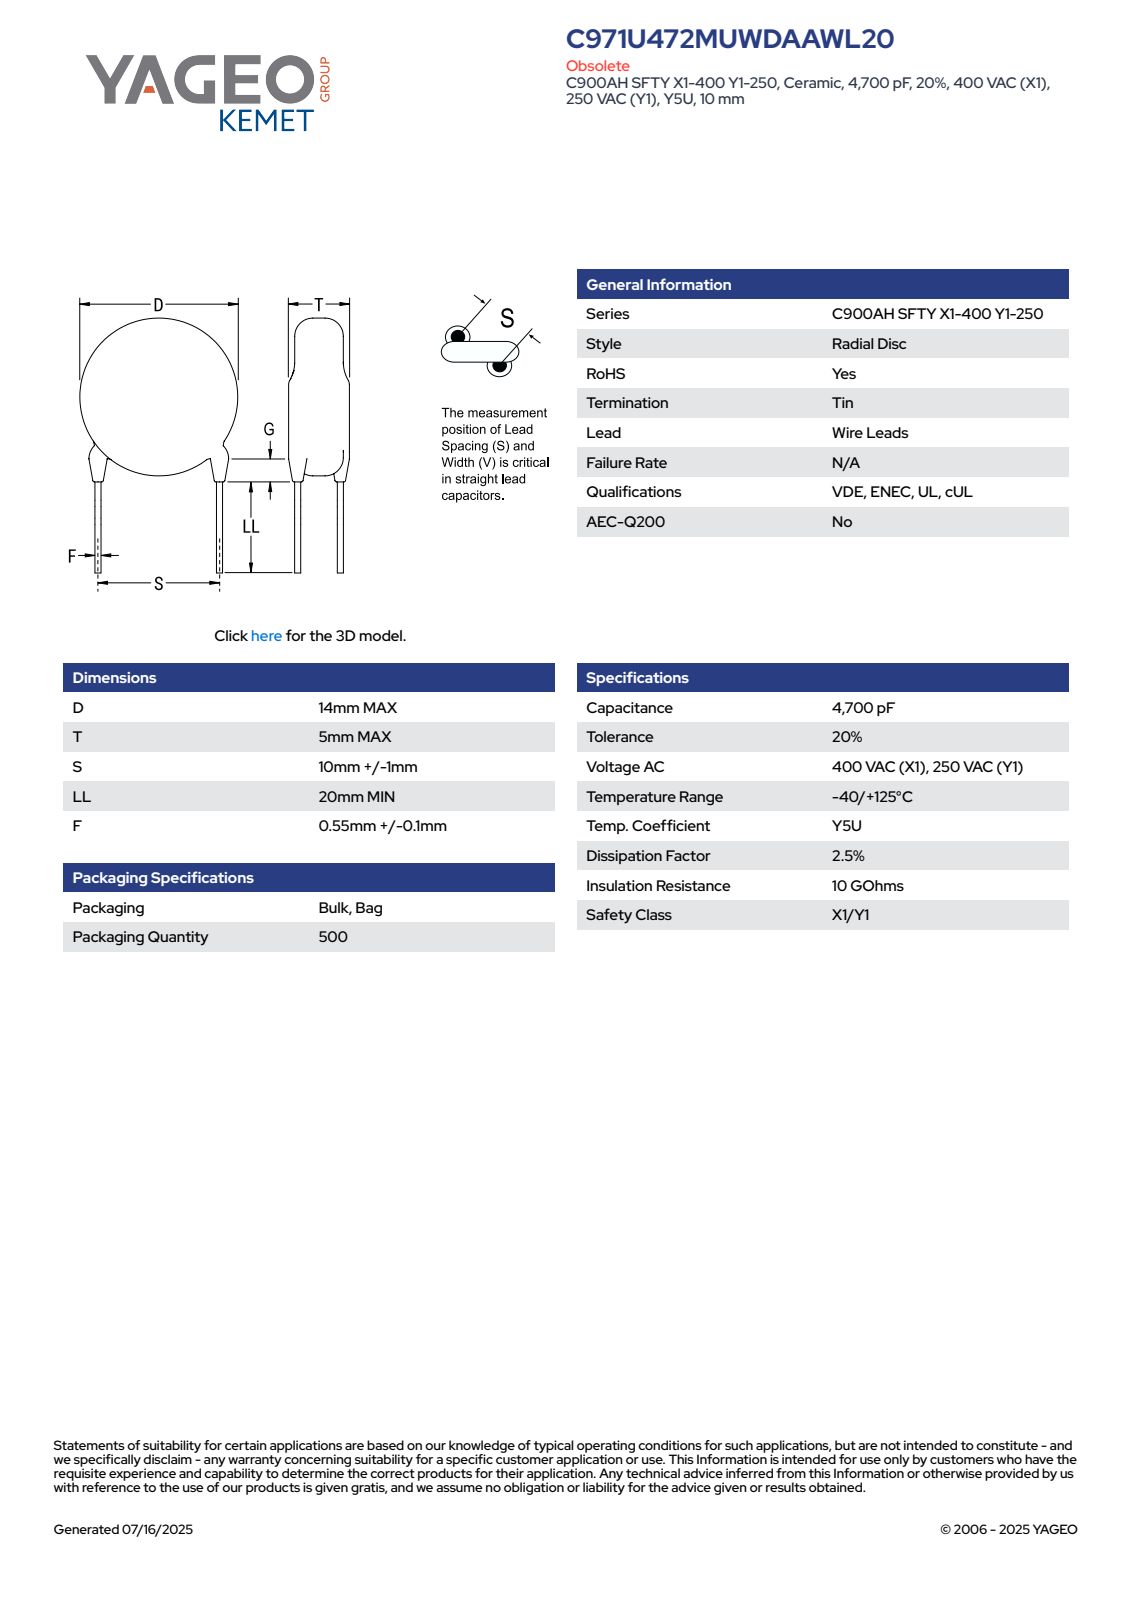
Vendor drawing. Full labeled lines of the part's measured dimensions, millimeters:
Part name (STEP PRODUCT): CCD_STC900_D14T5S10LL20F0.65G3
STEP written by: SolidWorks 2014 (AUTOMOTIVE_DESIGN)
Units: millimetres
Bodies: 4 solids, 83 faces (61 planar, 6 cylindrical, 16 other)
Overall size (bounding box): 34.29 × 14 × 5
Volume: 768 mm³ · Surface area: 596 mm²
Round bosses / shafts (diameter × count): ⌀0.65 ×2, ⌀14 ×1
Main face-to-face distances: 5, 28.09, 26.48, 1.61, 0.4, 6.61, 0.44, 0.6, 0.31, 1.3
